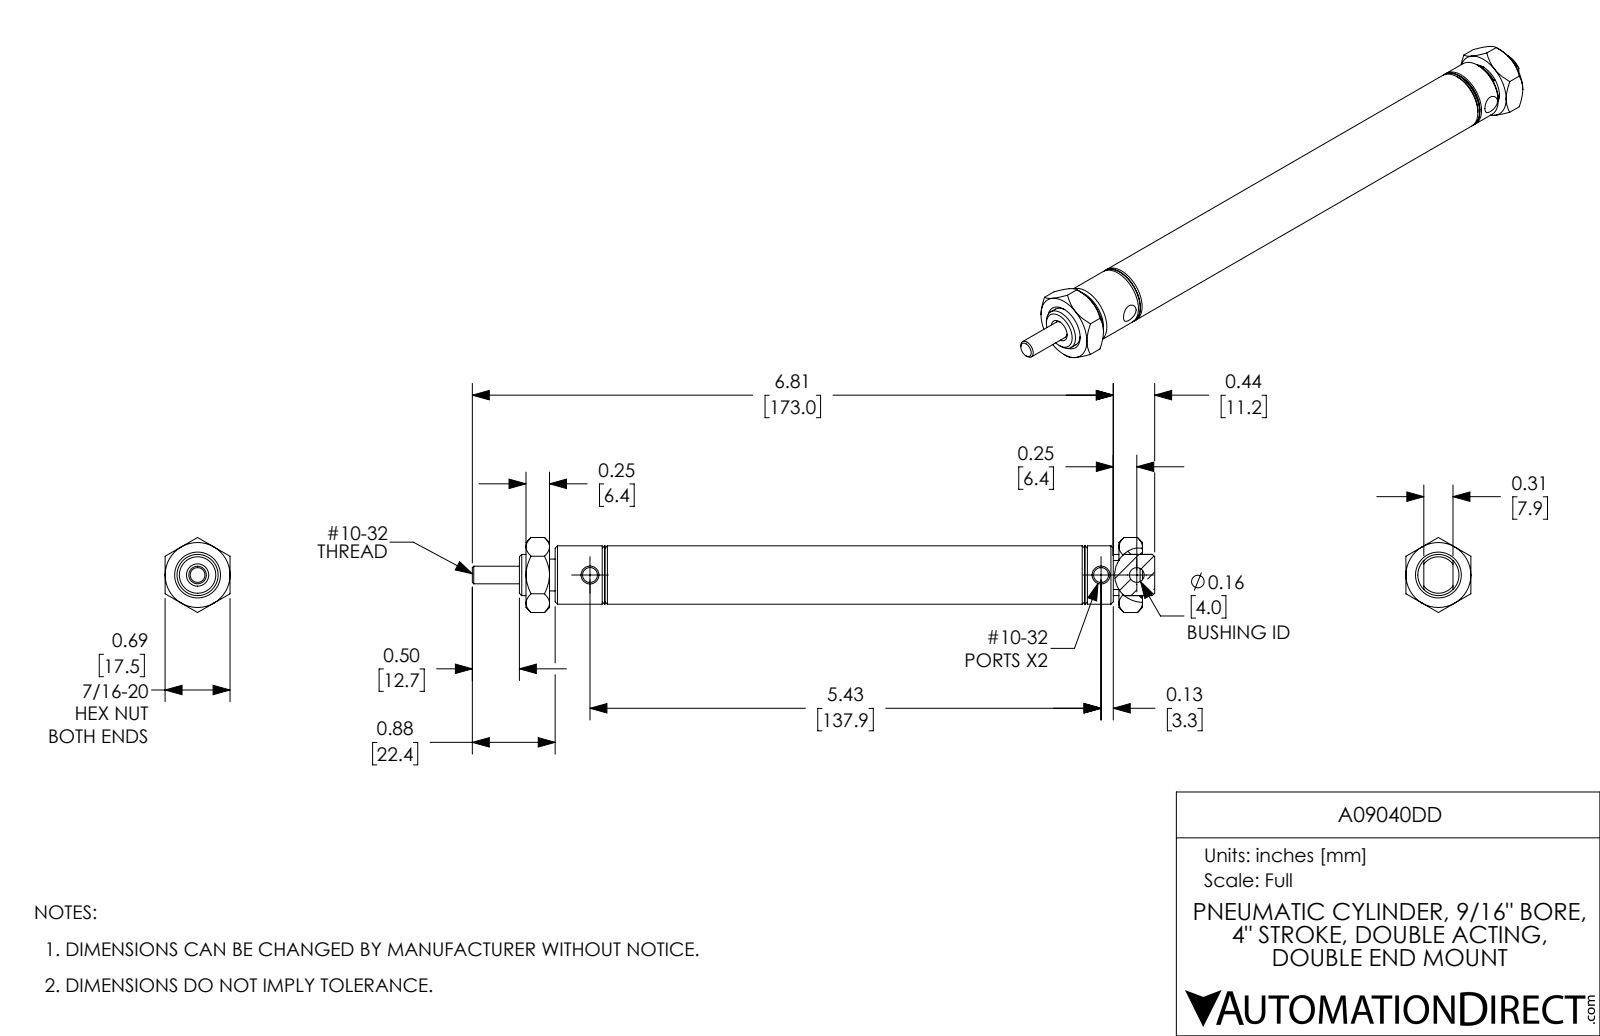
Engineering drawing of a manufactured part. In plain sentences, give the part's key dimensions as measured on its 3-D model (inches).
The part is named "A09040DD; A09040DD_Mounting Nut_D-154; A09040DD-Rod; A09040DD-MainBody". Its 3-D file was written by "SolidWorks 2017 (AUTOMOTIVE_DESIGN)". It is 4 solids with 151 faces: 36 planar, 46 cylindrical and 69 other. Overall it measures 7.25 by 0.797 by 0.69 inches. Its volume is 1.119 cubic inches and its surface area 30.54 square inches. Round holes: 2 of diameter 0.159, 2 of diameter 0.19, 1 of diameter 0.156, 1 of diameter 0.157, 1 of diameter 0.187, 1 of diameter 0.563. Round bosses or shafts: 1 of diameter 0.62, 1 of diameter 0.437, 1 of diameter 0.338. The main face-to-face distances are 0.69, 0.5, 0.25, 6.3, 0.715, 5.215, 5.275, 0.31, 4.5, 0.775. The hole center spacings are 0.38, 5.43, 5.81.
